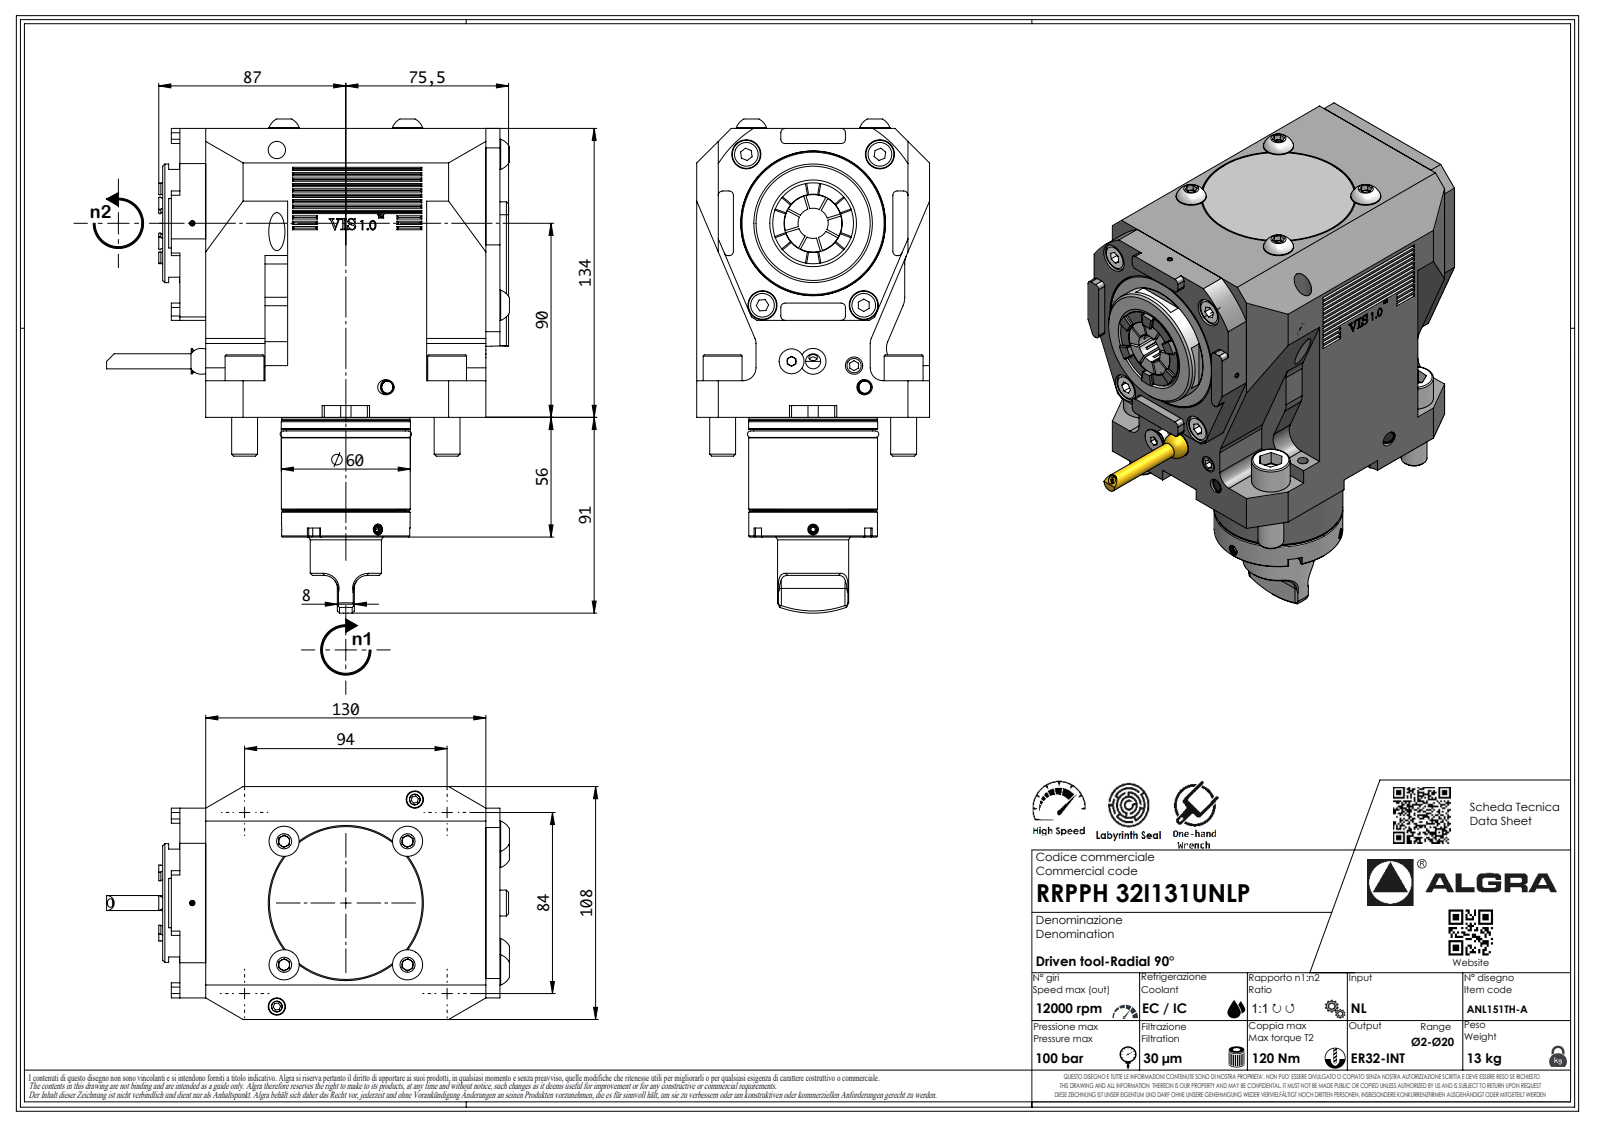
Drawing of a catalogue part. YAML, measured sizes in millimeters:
part_name: "RRPPH32I131UNLP"
step_written_by: "SolidWorks 2023 (AUTOMOTIVE_DESIGN)"
units: millimeters
bodies: {solids: 1, faces: 643, planar: 390, cylindrical: 116, other: 137}
overall_size: [224.8, 186.5, 108]
volume: 1988000
surface_area: 123661
round_holes:
  - {diameter: 2.1, count: 1}
round_bosses_or_shafts:
  - {diameter: 18, count: 4}
  - {diameter: 12, count: 4}
  - {diameter: 59.9, count: 1}
  - {diameter: 59.8, count: 1}
  - {diameter: 59.7, count: 1}
  - {diameter: 59.5, count: 1}
  - {diameter: 55.2, count: 1}
  - {diameter: 55, count: 1}
partial_cylinders:
  - {radius: 8, count: 22}
  - {radius: 2, count: 16}
  - {radius: 0.33, count: 7}
  - {radius: 0.52, count: 7}
  - {radius: 3.7, count: 7}
  - {radius: 6, count: 7}
  - {radius: 10, count: 4}
  - {radius: 3, count: 3}
face_to_face_distances: [108, 134, 12, 29, 101, 148.5, 136.5, 49, 72, 5.5]
